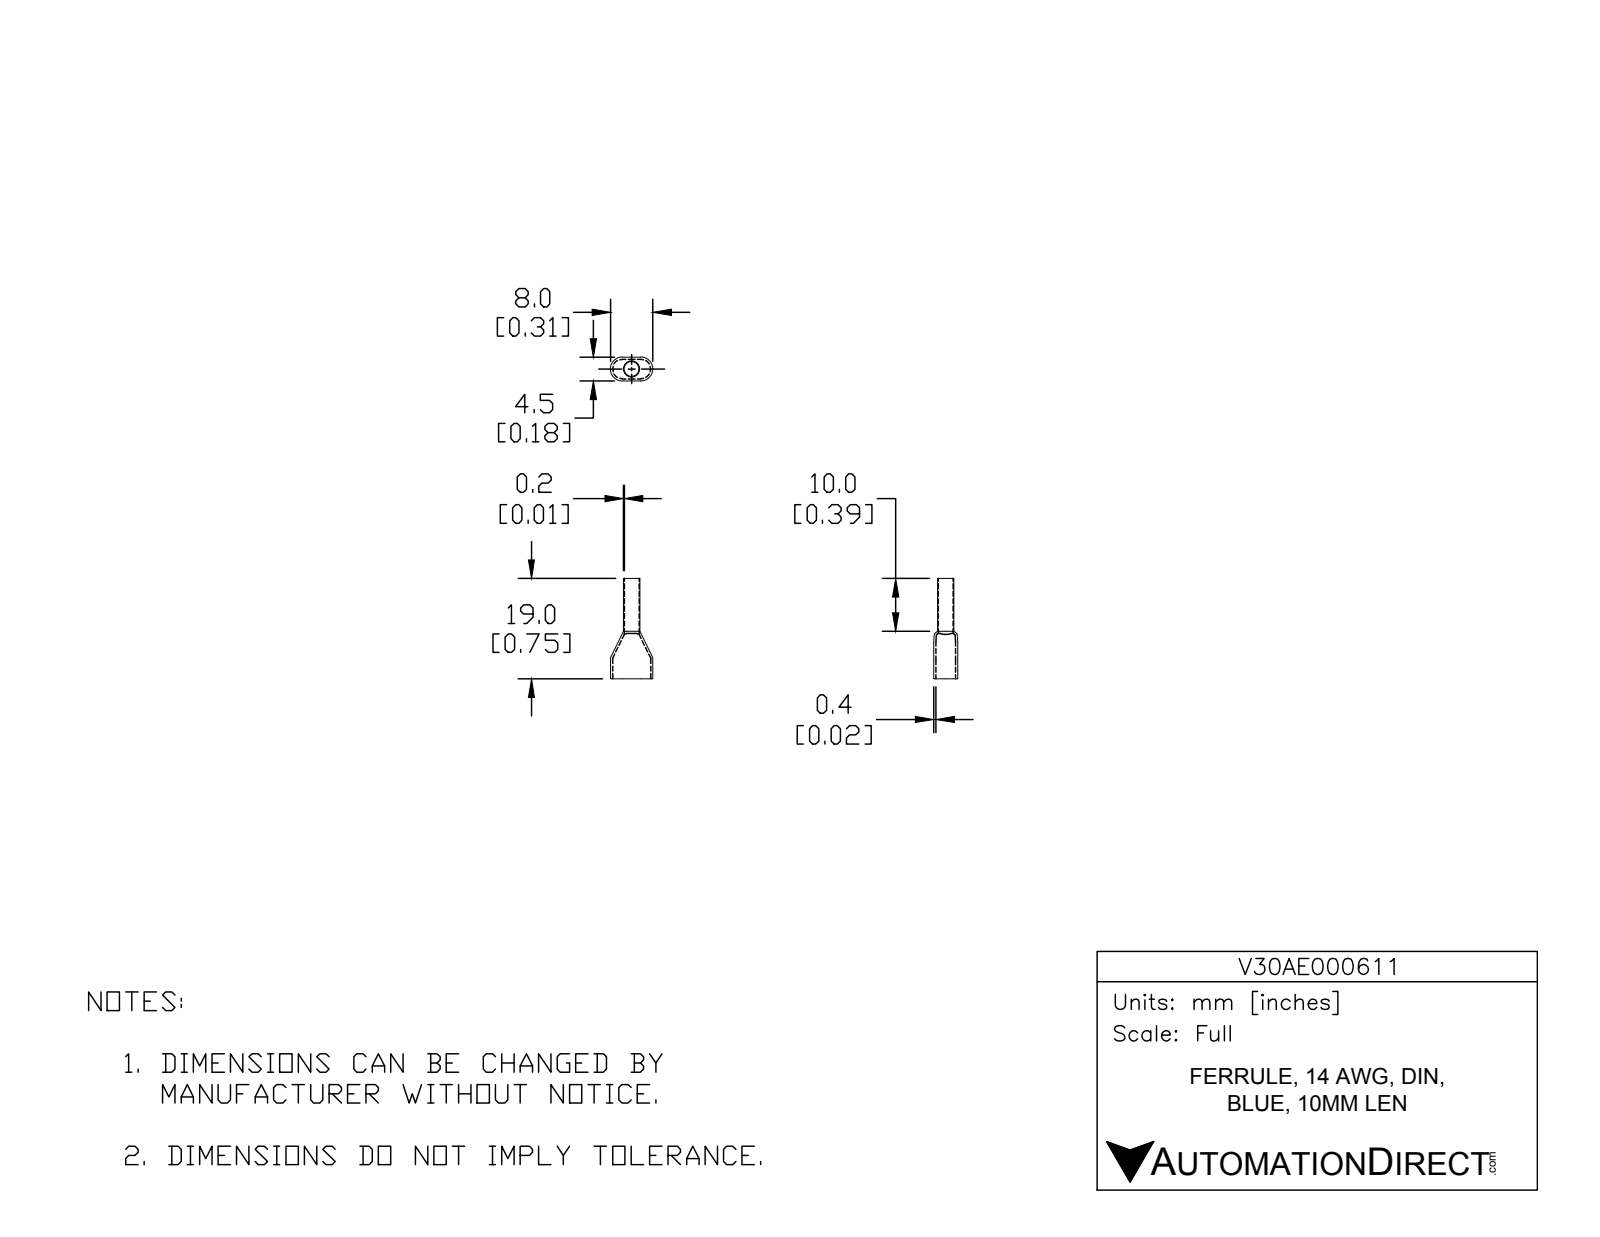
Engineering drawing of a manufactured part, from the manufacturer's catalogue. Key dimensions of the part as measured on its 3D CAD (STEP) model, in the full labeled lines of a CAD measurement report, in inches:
Part name (STEP PRODUCT): V30AE000611
STEP written by: SolidWorks 2017 (AUTOMOTIVE_DESIGN)
Units: inches
Bodies: 2 solids, 36 faces (14 planar, 22 cylindrical, 0 other)
Overall size (bounding box): 0.748 × 0.315 × 0.177
Volume: 0.005 in³ · Surface area: 0.794 in²
Round holes (diameter × count): ⌀0.11 ×1
Round bosses / shafts (diameter × count): ⌀0.122 ×1
Partial cylindrical surfaces — rounded edges, fillets, slot ends (radius × count): R0.073 ×4, R0.089 ×4
Main face-to-face distances: 0.016, 0.161, 0.177, 0.146, 0.354, 0.748, 0.394, 0.339, 0.409
